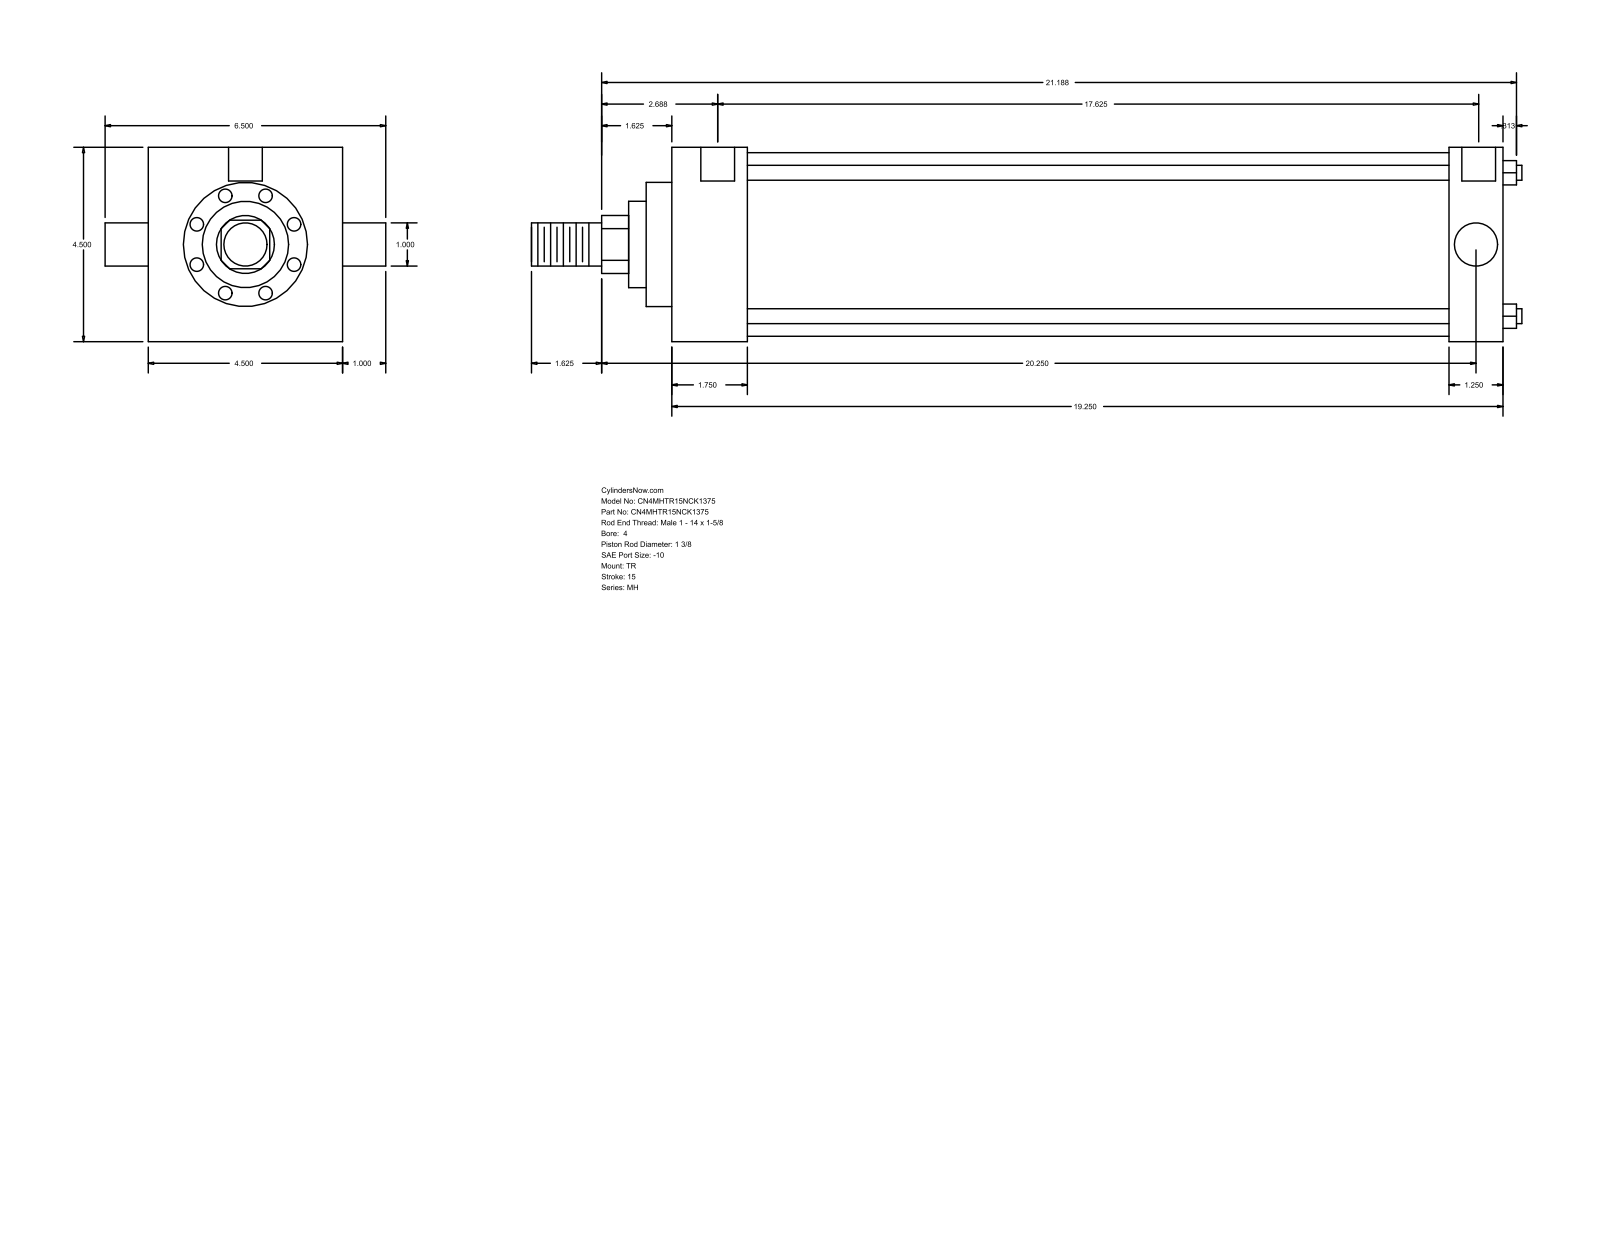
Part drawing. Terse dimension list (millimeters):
name: MH_TR__0400_1.375
written by: GSSL Pune (CONFIG_CONTROL_DESIGN)
unit: mm
bodies: 0 solids, 86 faces (61 planar, 25 cylindrical, 0 other)
size: 582.61 × 165.1 × 114.3
holes: 3× ⌀8.73, 2× ⌀19.84
bosses: 4× ⌀8.76, 2× ⌀25.4, 1× ⌀107.95, 1× ⌀73.03, 1× ⌀50.8, 1× ⌀34.92
rounds: 1× R17.06
face distances: 114.3, 488.96, 44.45, 444.51, 457.21, 412.76, 31.75, 15.08, 59.53, 472.29
hole spacings: 1.58, 1.59, 447.68, 449.26, 449.27, 450.85
